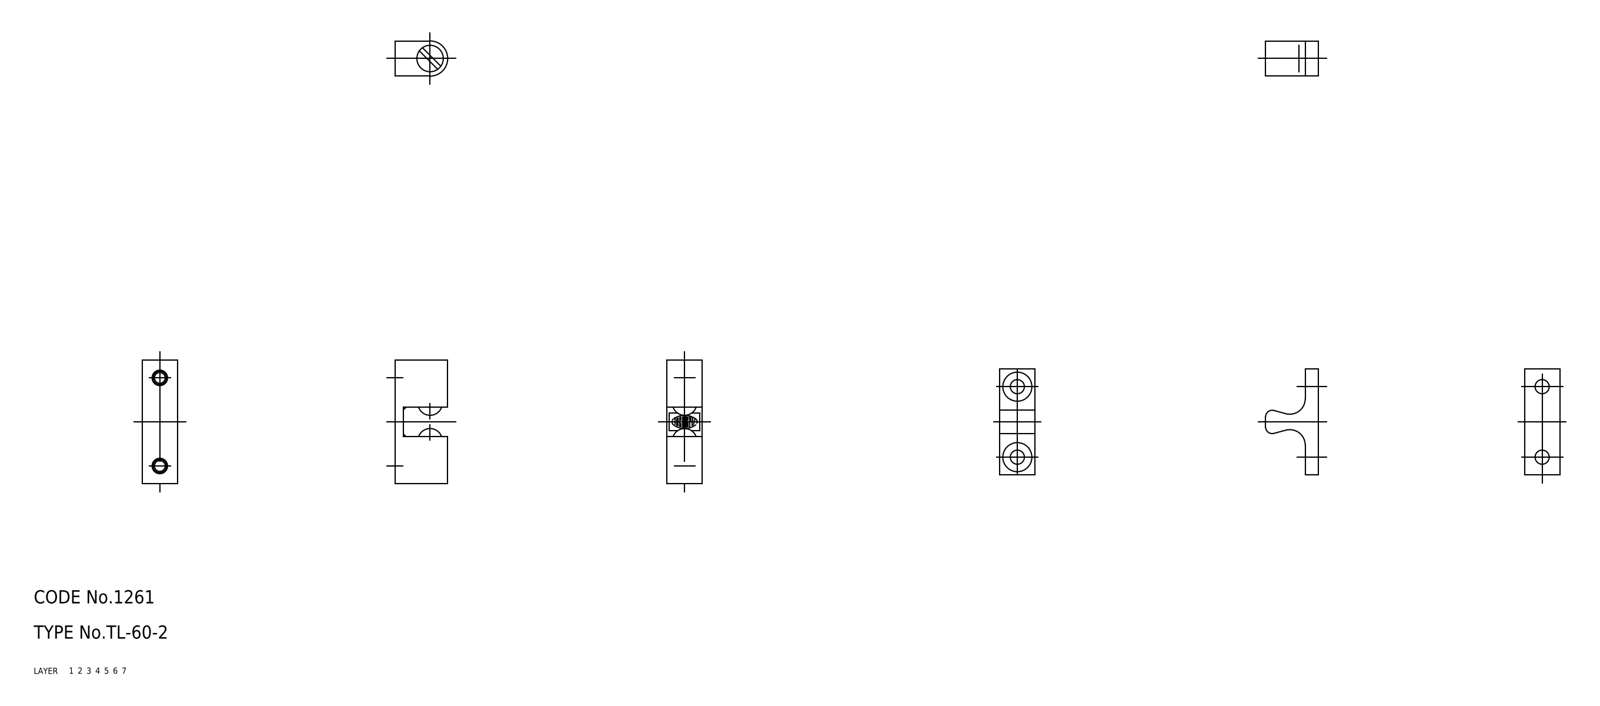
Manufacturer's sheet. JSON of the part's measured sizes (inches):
{"part_name": "screw; ball; keeper; housing (+1 more)", "step_written_by": "CADfix (AUTOMOTIVE_DESIGN)", "units": "inches", "bodies": {"solids": 6, "faces": 68, "planar": 0, "cylindrical": 0, "other": 68}, "overall_size": [1.449, 1.102, 0.315], "volume_in3": 0.167, "surface_area_in2": 4.697}
